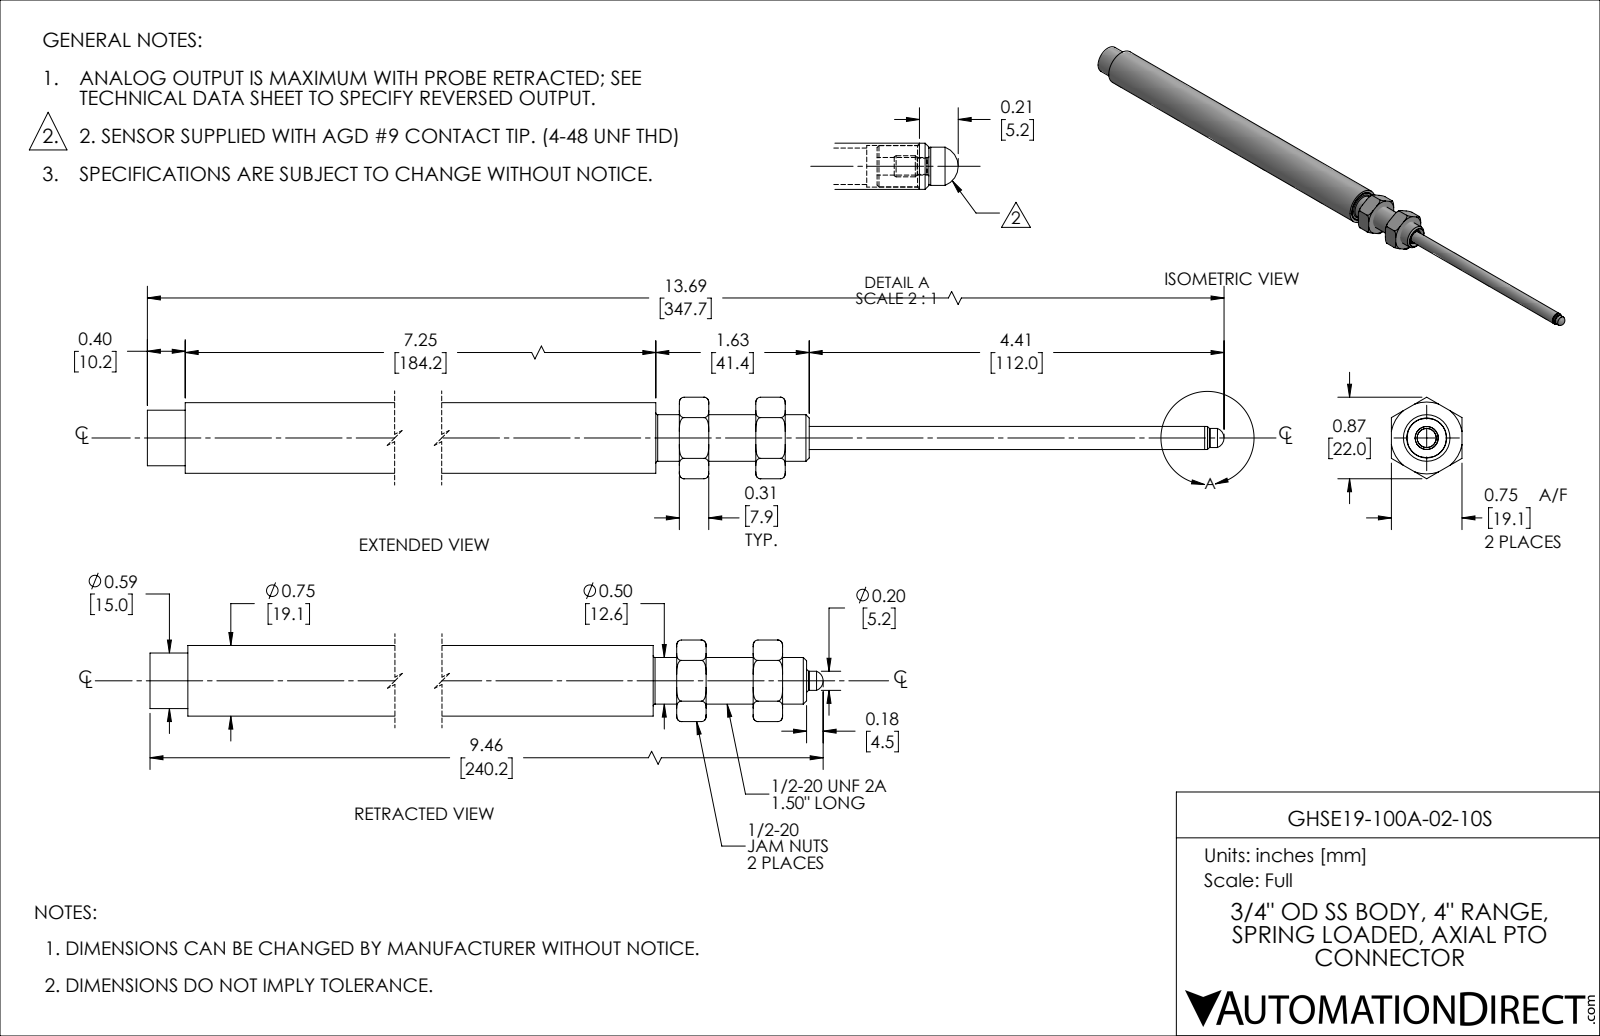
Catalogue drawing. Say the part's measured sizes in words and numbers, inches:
The part is named "GHSE19-100A-02-10S". Its 3-D file was written by "SolidWorks 2019 (AUTOMOTIVE_DESIGN)". It is 11 solids with 187 faces: 77 planar, 65 cylindrical and 45 other. Overall it measures 9.458 by 0.866 by 0.75 inches. Its volume is 1.781 cubic inches and its surface area 57.58 square inches. Round holes: 1 of diameter 0.093, 1 of diameter 0.156, 1 of diameter 0.193, 1 of diameter 0.221, 1 of diameter 0.249, 1 of diameter 0.302, 1 of diameter 0.31, 1 of diameter 0.453, 1 of diameter 0.52, 1 of diameter 0.62, 1 of diameter 0.625, 1 of diameter 0.65. Round bosses or shafts: 6 of diameter 0.03, 1 of diameter 0.75, 1 of diameter 0.725, 1 of diameter 0.672, 1 of diameter 0.624, 1 of diameter 0.59, 1 of diameter 0.495, 1 of diameter 0.375. Partial cylindrical surfaces (rounded edges, fillets, slot ends): 2 of radius 0.011, 2 of radius 0.04, 1 of radius 0.133, 1 of radius 0.156, 1 of radius 0.275. The main face-to-face distances are 0.75, 0.812, 0.313, 0.813, 1.125, 0.5, 0.312, 0.75, 7.522, 7.835.
